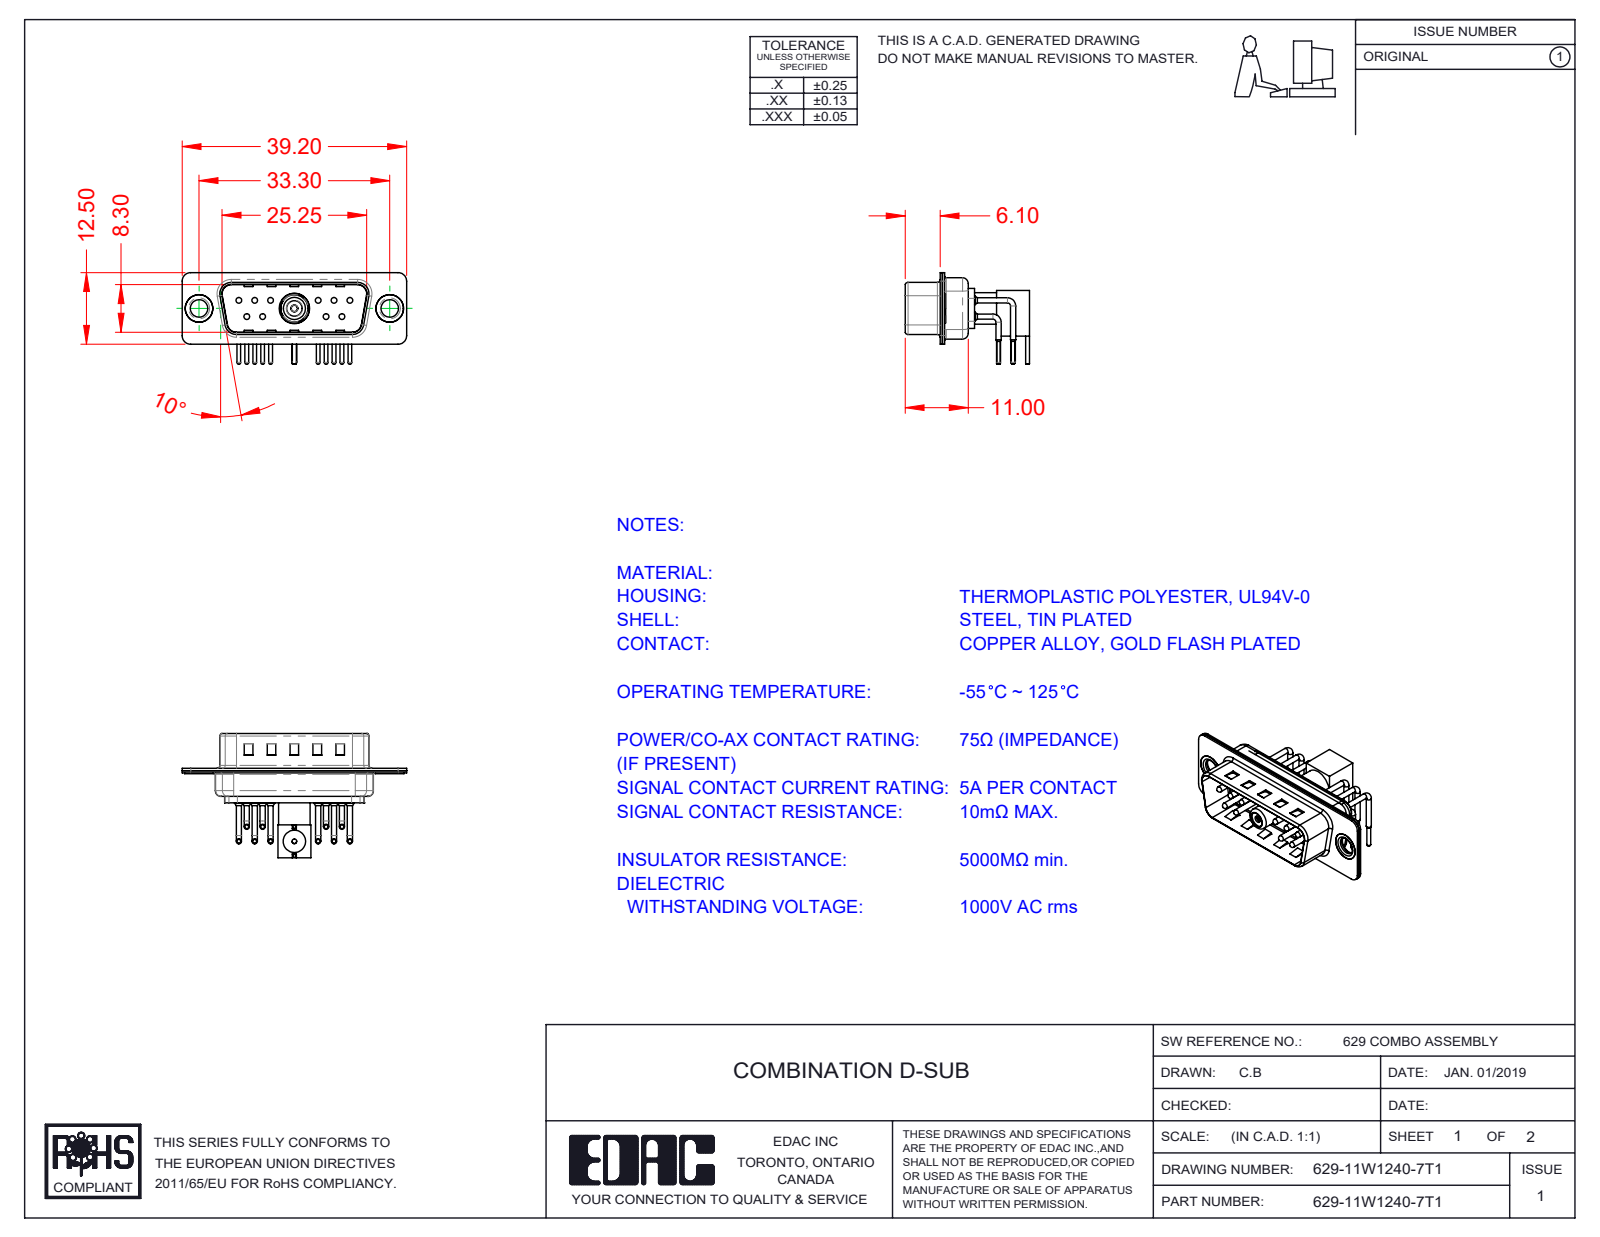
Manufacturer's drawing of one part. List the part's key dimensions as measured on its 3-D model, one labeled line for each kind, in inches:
Part name (STEP PRODUCT): Insulator Socket; 629Combo Contact Row 2; 629Combo Shell Front_15 Contacts; 629Combo Contact Row 1 (+8 more)
STEP written by: SolidWorks 2020 (CONFIG_CONTROL_DESIGN)
Units: inches
Bodies: 22 solids, 1579 faces (845 planar, 548 cylindrical, 186 other)
Overall size (bounding box): 1.543 × 0.855 × 0.63
Volume: 0.13 in³ · Surface area: 9.196 in²
Round holes (diameter × count): ⌀0.063 ×11, ⌀0.03 ×10, ⌀0.079 ×10, ⌀0.12 ×2, ⌀0.157 ×2, ⌀0.189 ×2, ⌀0.031 ×1, ⌀0.043 ×1, ⌀0.047 ×1, ⌀0.059 ×1, ⌀0.098 ×1, ⌀0.106 ×1
Round bosses / shafts (diameter × count): ⌀0.035 ×20, ⌀0.059 ×10, ⌀0.039 ×10, ⌀0.026 ×10, ⌀0.197 ×2, ⌀0.193 ×2, ⌀0.14 ×2, ⌀0.031 ×2
Partial cylindrical surfaces — rounded edges, fillets, slot ends (radius × count): R0.059 ×16, R0.079 ×12, R0.04 ×10, R0.02 ×8, R0.063 ×8, R0.039 ×7, R0.01 ×4, R0.024 ×4
Main face-to-face distances: 0.016, 0.031, 0.374, 0.358, 0.343, 0.014, 0.39, 0.03, 0.047, 0.236
Hole centre spacings: 0.124, 0.109, 0.545, 0.436, 0.654, 0.198, 0.198, 0.218
